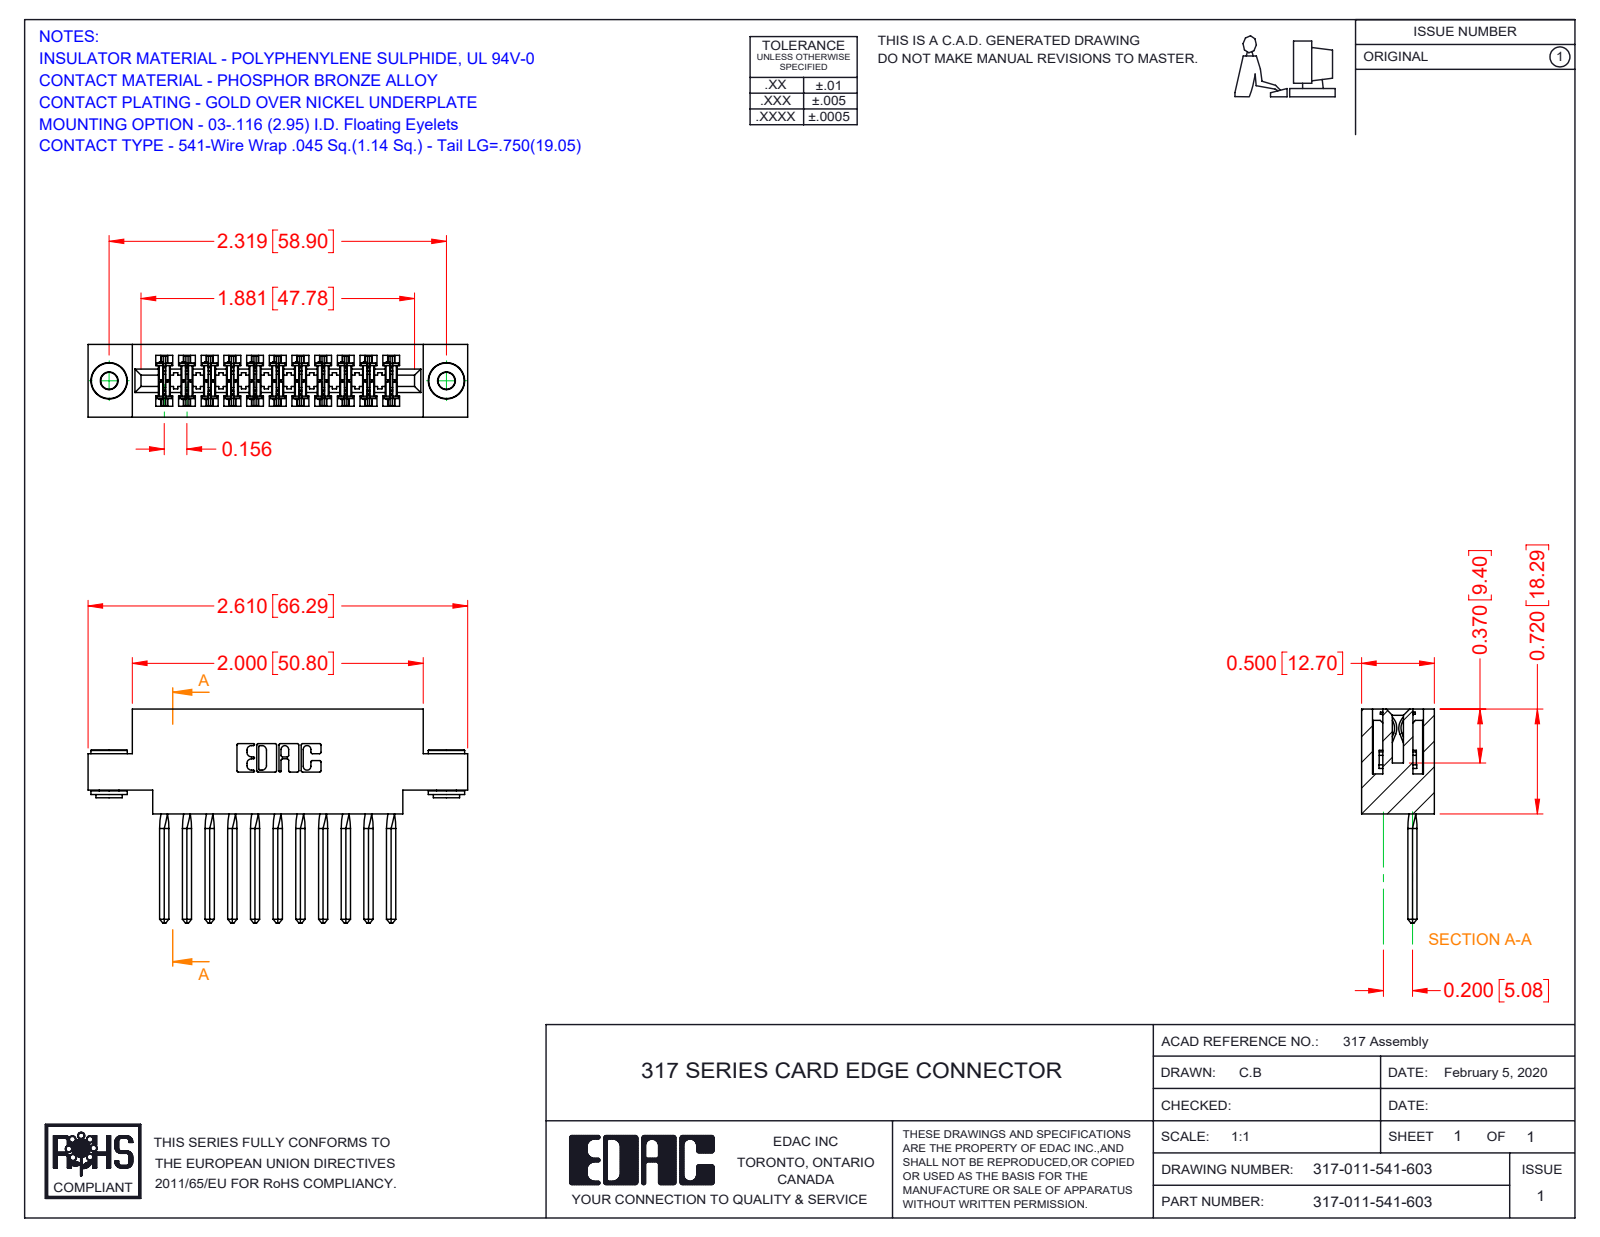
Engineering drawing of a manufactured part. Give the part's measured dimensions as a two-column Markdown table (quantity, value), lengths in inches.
| quantity | value |
| --- | --- |
| part name | 317 Part_.156 Dia - TH; 317-290-002_541; 345-250-002_345-250-002-102; 317-011-541-603 |
| STEP written by | SolidWorks 2016 (CONFIG_CONTROL_DESIGN) |
| units | inches |
| bodies | 14 solids, 1812 faces (1432 planar, 328 cylindrical, 52 other) |
| overall size | 2.61 × 1.47 × 0.5 |
| volume | 0.599 in³ |
| surface area | 20.23 in² |
| round holes (diameter × count) | 0.116 × 2, 0.156 × 2 |
| round bosses / shafts (diameter × count) | 0.25 × 2, 0.18 × 2, 0.136 × 2 |
| partial cylindrical surfaces (radius × count) | 0.01 × 22, 0.015 × 22, 0.007 × 6, 0.031 × 6, 0.026 × 3, 0.095 × 2, 0.1 × 2, 0.11 × 2 |
| main face-to-face distances | 0.5, 0.075, 0.425, 0.11, 0.22, 0.065, 0.35, 0.331, 0.156, 0.176 |
| hole center spacings | 2.319 |
